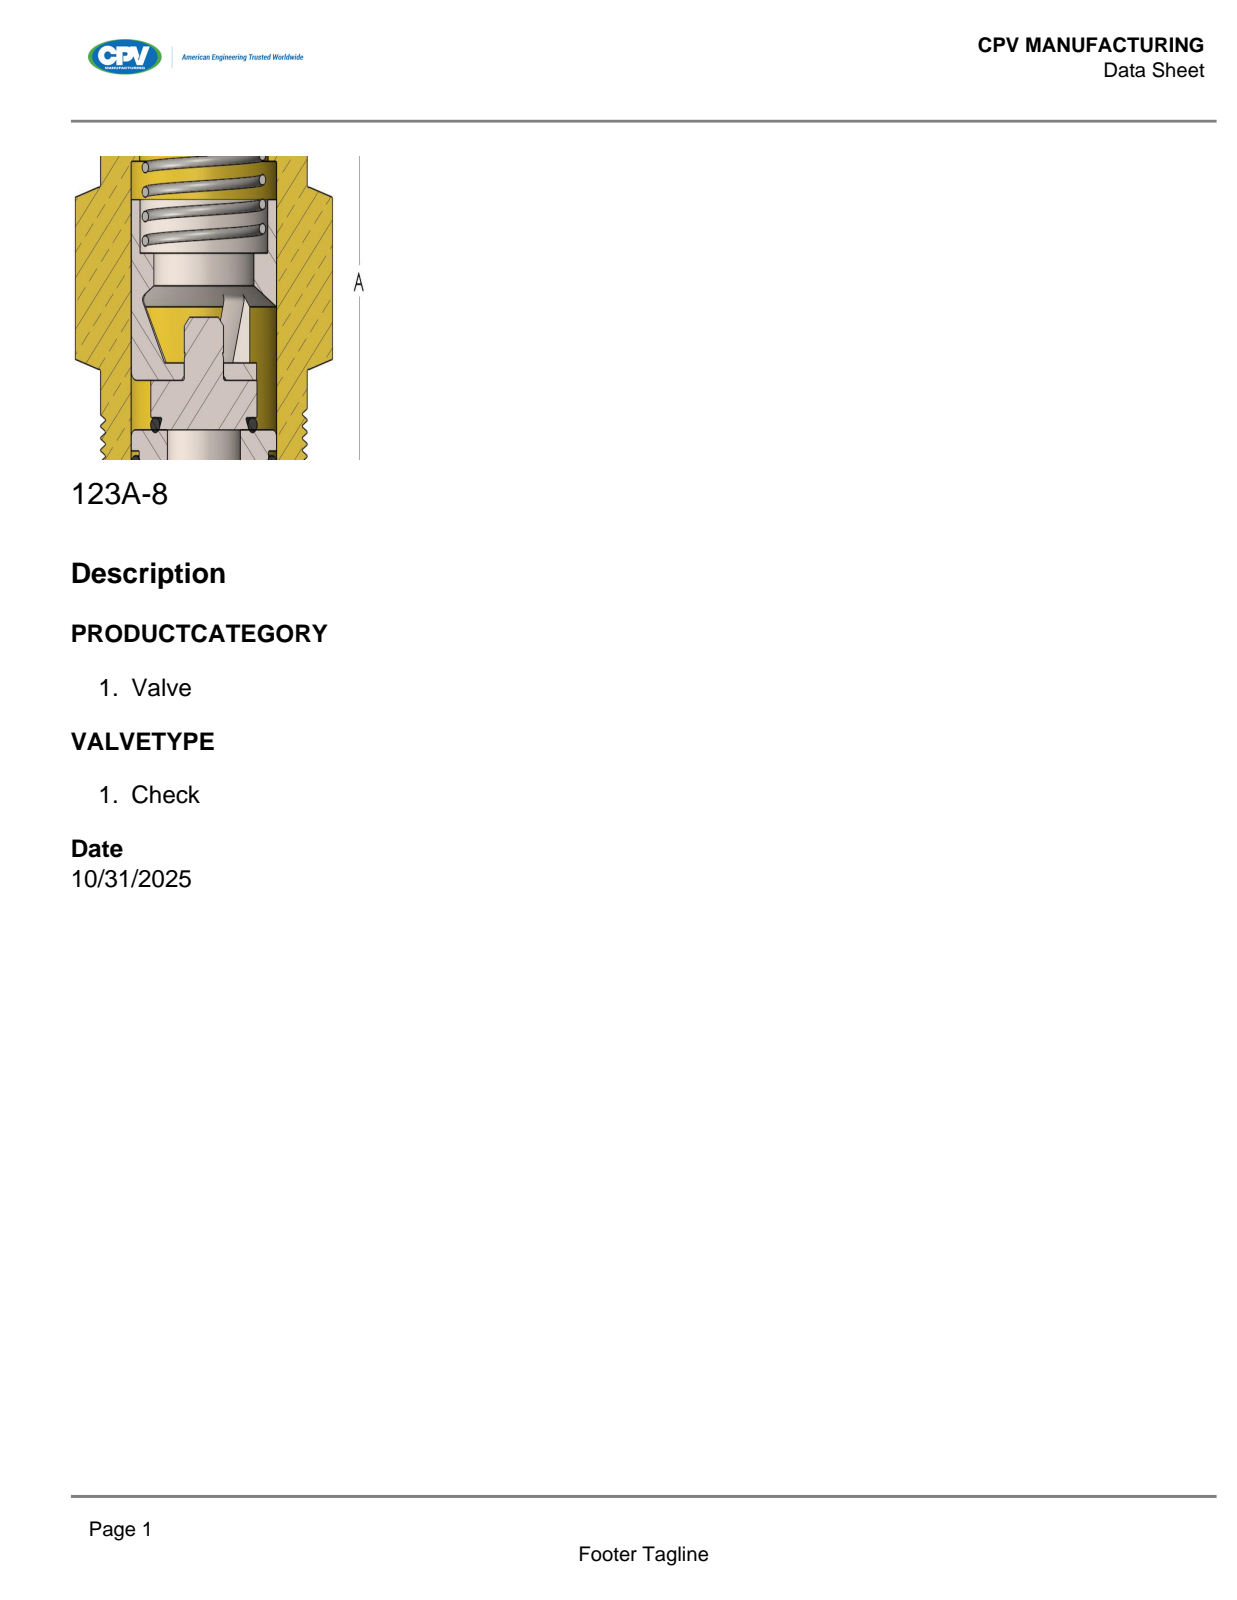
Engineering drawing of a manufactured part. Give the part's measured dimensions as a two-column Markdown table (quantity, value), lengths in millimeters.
| quantity | value |
| --- | --- |
| part name | 123A-8 |
| STEP written by | SolidWorks 2018 (AUTOMOTIVE_DESIGN) |
| units | millimeters |
| bodies | 1 solid, 71 faces (11 planar, 44 cylindrical, 16 other) |
| overall size | 114.3 × 104.9 × 102 |
| volume | 836 100 mm³ |
| surface area | 62 390 mm² |
| round holes (diameter × count) | 42.9 × 1, 44.5 × 1 |
| round bosses / shafts (diameter × count) | 95.1 × 1, 72.8 × 1 |
| partial cylindrical surfaces (radius × count) | 57.2 × 1 |
| main face-to-face distances | 76.2, 25.4, 50.8, 25.8, 76.6, 102, 0.4, 101.6, 104.9, 97.2 |
